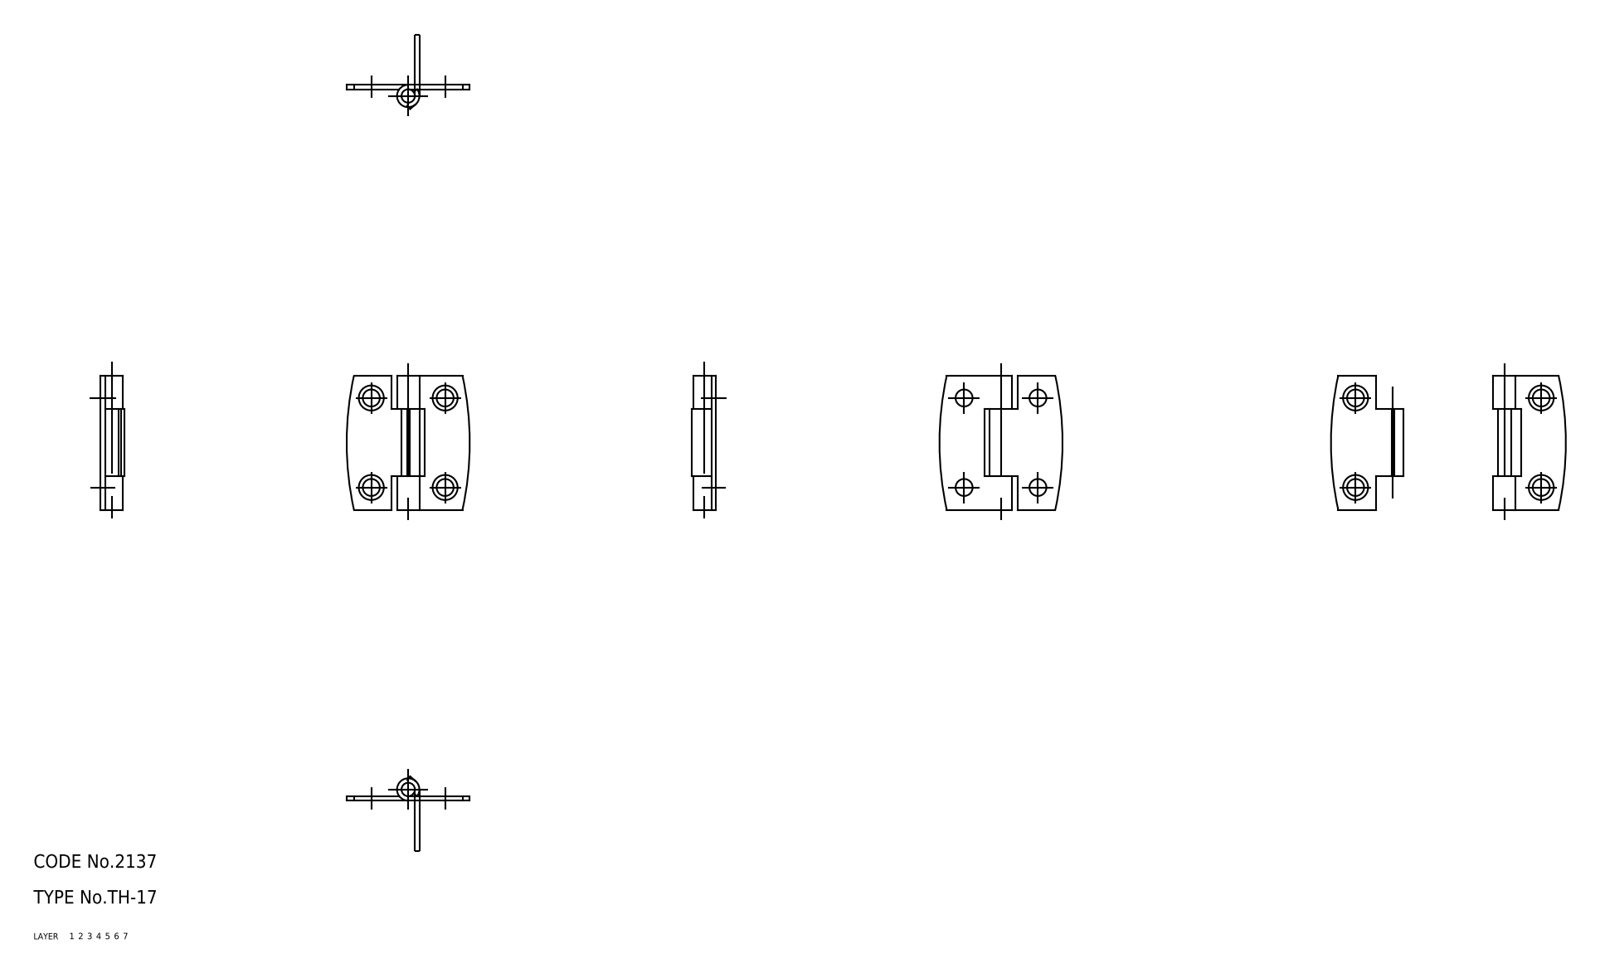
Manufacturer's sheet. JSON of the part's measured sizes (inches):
{"part_name": "shaft; hinge piece_B; hinge piece_A; TH_17_5826_36", "step_written_by": "CADfix (AUTOMOTIVE_DESIGN)", "units": "inches", "bodies": {"solids": 3, "faces": 48, "planar": 0, "cylindrical": 0, "other": 48}, "overall_size": [1.181, 1.083, 0.213], "volume_in3": 0.066, "surface_area_in2": 3.624}
